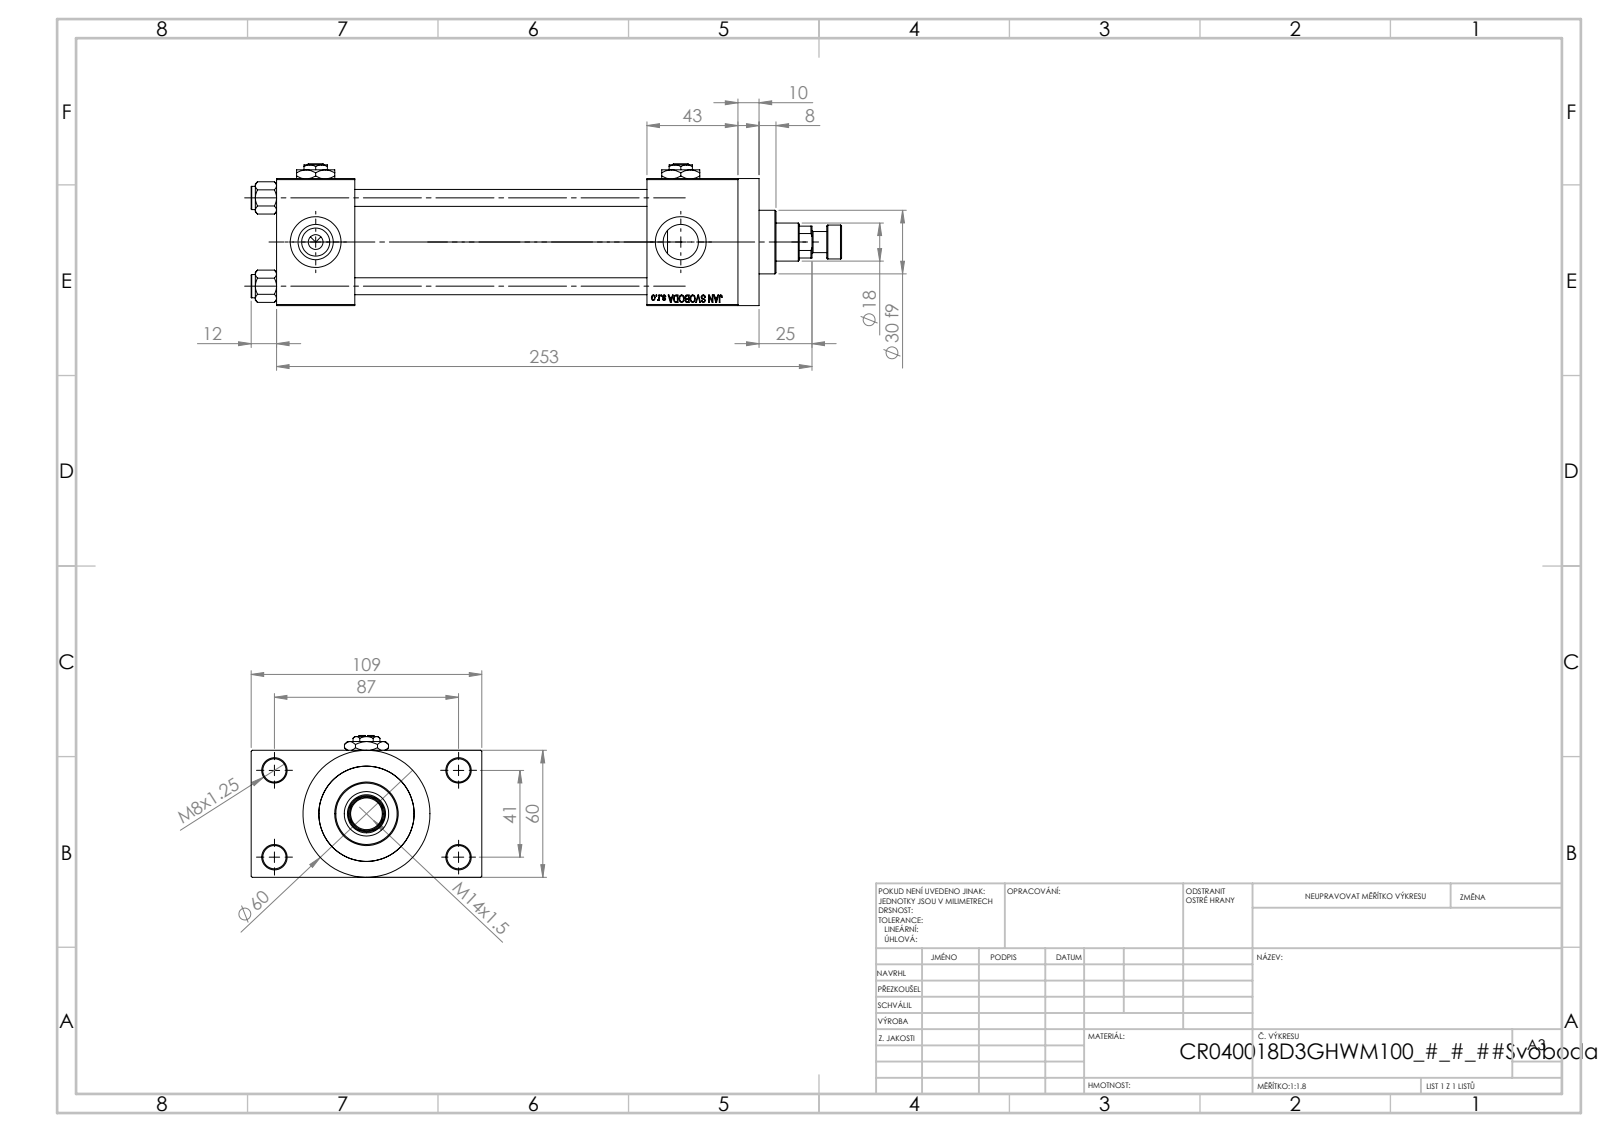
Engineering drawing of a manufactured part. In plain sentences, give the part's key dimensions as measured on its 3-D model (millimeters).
The part is named "V215CR_D_TYCINKA; V215_VC_A; Zatka_pro_OIL_PORT; V215CR_VCP_D (+3 more)". Its 3-D file was written by "SolidWorks 2019 (CONFIG_CONTROL_DESIGN)". It is 14 solids with 1218 faces: 549 planar, 103 cylindrical and 566 other. Overall it measures 279 by 109 by 67 millimeters. Its volume is 581 157 cubic millimeters and its surface area 160 349 square millimeters. Round holes: 4 of diameter 8, 4 of diameter 11, 4 of diameter 16.66, 4 of diameter 24, 3 of diameter 7, 1 of diameter 8.5, 1 of diameter 18, 1 of diameter 21, 1 of diameter 31, 1 of diameter 40, 1 of diameter 45. Round bosses or shafts: 4 of diameter 11, 1 of diameter 60, 1 of diameter 46, 1 of diameter 30, 1 of diameter 16, 1 of diameter 10. Partial cylindrical surfaces (rounded edges, fillets, slot ends): 1 of radius 8.5. The main face-to-face distances are 60, 24.5, 138, 84.5, 37, 175, 43, 218, 181, 10. The hole center spacings are 22.65, 29.49, 41.7, 47.15, 48.09, 64.35, 76.49, 41.
